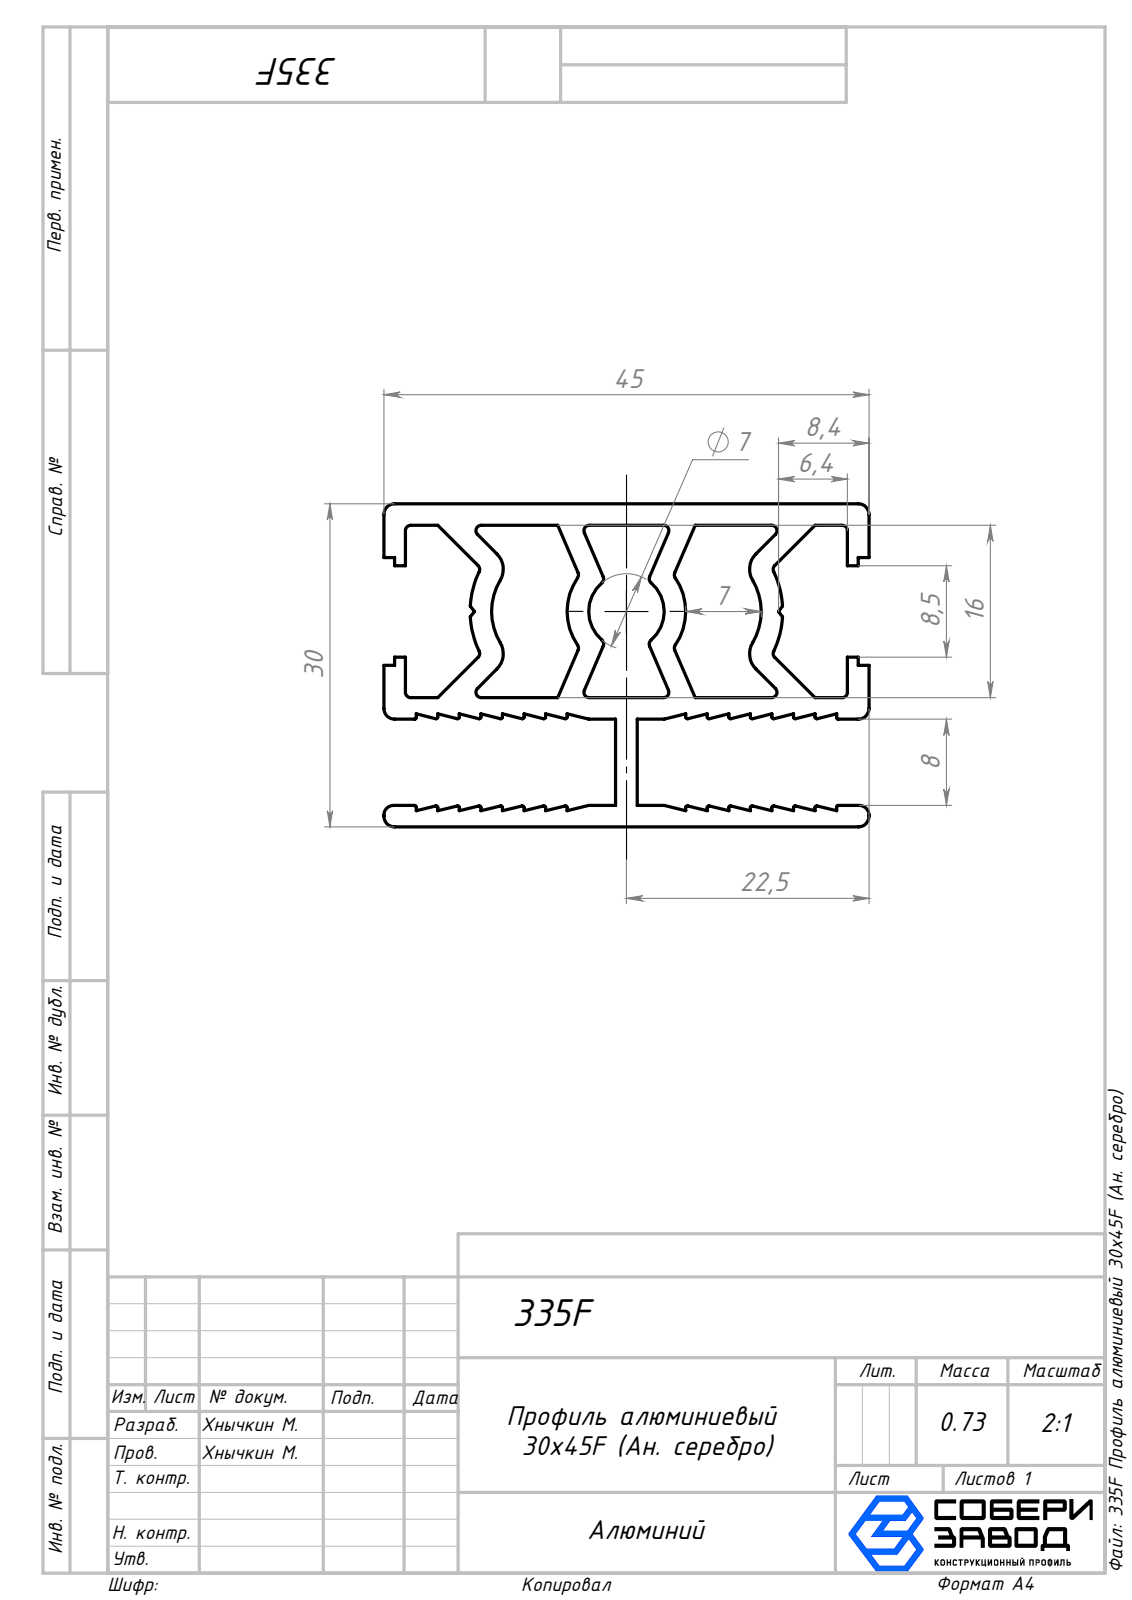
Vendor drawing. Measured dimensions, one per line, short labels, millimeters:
name: 335F Профиль алюминиевый 30х45F (Ан. серебро)
written by: SolidWorks 2026 (AUTOMOTIVE_DESIGN)
unit: mm
bodies: 1 solid, 223 faces (130 planar, 93 cylindrical, 0 other)
size: 610 × 45 × 30
volume: 271 382 mm³; area: 278 010 mm²
rounds: 32× R0.15, 24× R0.5, 6× R1, 4× R2, 2× R0.9, 2× R5.69, 2× R8.5, 1× R3.5
face distances: 2, 30, 0.97, 28, 18, 0.48, 1.94, 2.67, 21.5, 12
